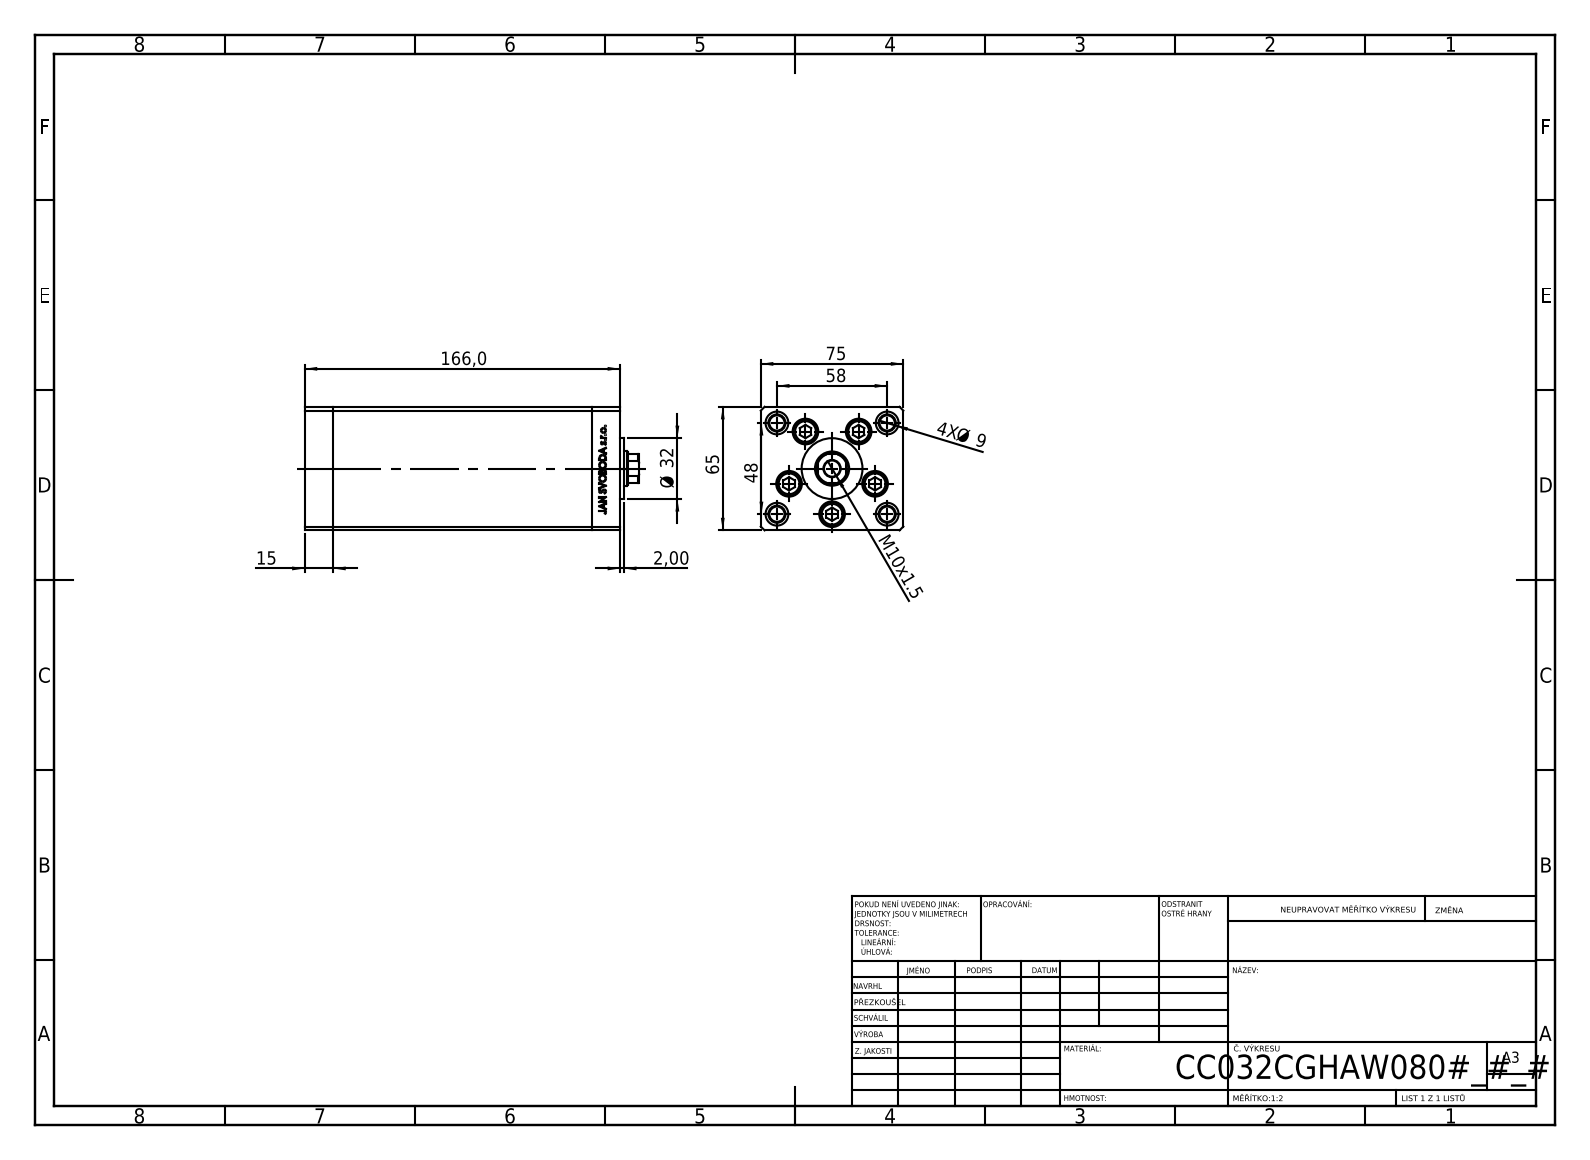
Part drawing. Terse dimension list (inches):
name: V220C_VC_C; ALLEN BOLT; V220C FRONT; V220C BACK_C (+1 more)
written by: SolidWorks 2019 (CONFIG_CONTROL_DESIGN)
unit: in
bodies: 13 solids, 1179 faces (542 planar, 175 cylindrical, 462 other)
size: 6.929 × 2.953 × 2.559
volume: 41.31 in³; area: 222.8 in²
holes: 9× ⌀0.354, 5× ⌀0.531, 4× ⌀0.079, 4× ⌀0.315, 4× ⌀0.472, 4× ⌀0.518, 1× ⌀0.335, 1× ⌀0.492, 1× ⌀0.709
bosses: 5× ⌀0.315, 4× ⌀0.492, 1× ⌀1.26
rounds: 2× R0.037, 1× R0.335
face distances: 2.953, 2.559, 0.591, 5.354, 5.945, 6.535, 1.102, 0.512, 5.591, 0.354
hole spacings: 0.945, 1.482, 0.617, 0.678, 1.091, 1.135, 1.142, 1.285
